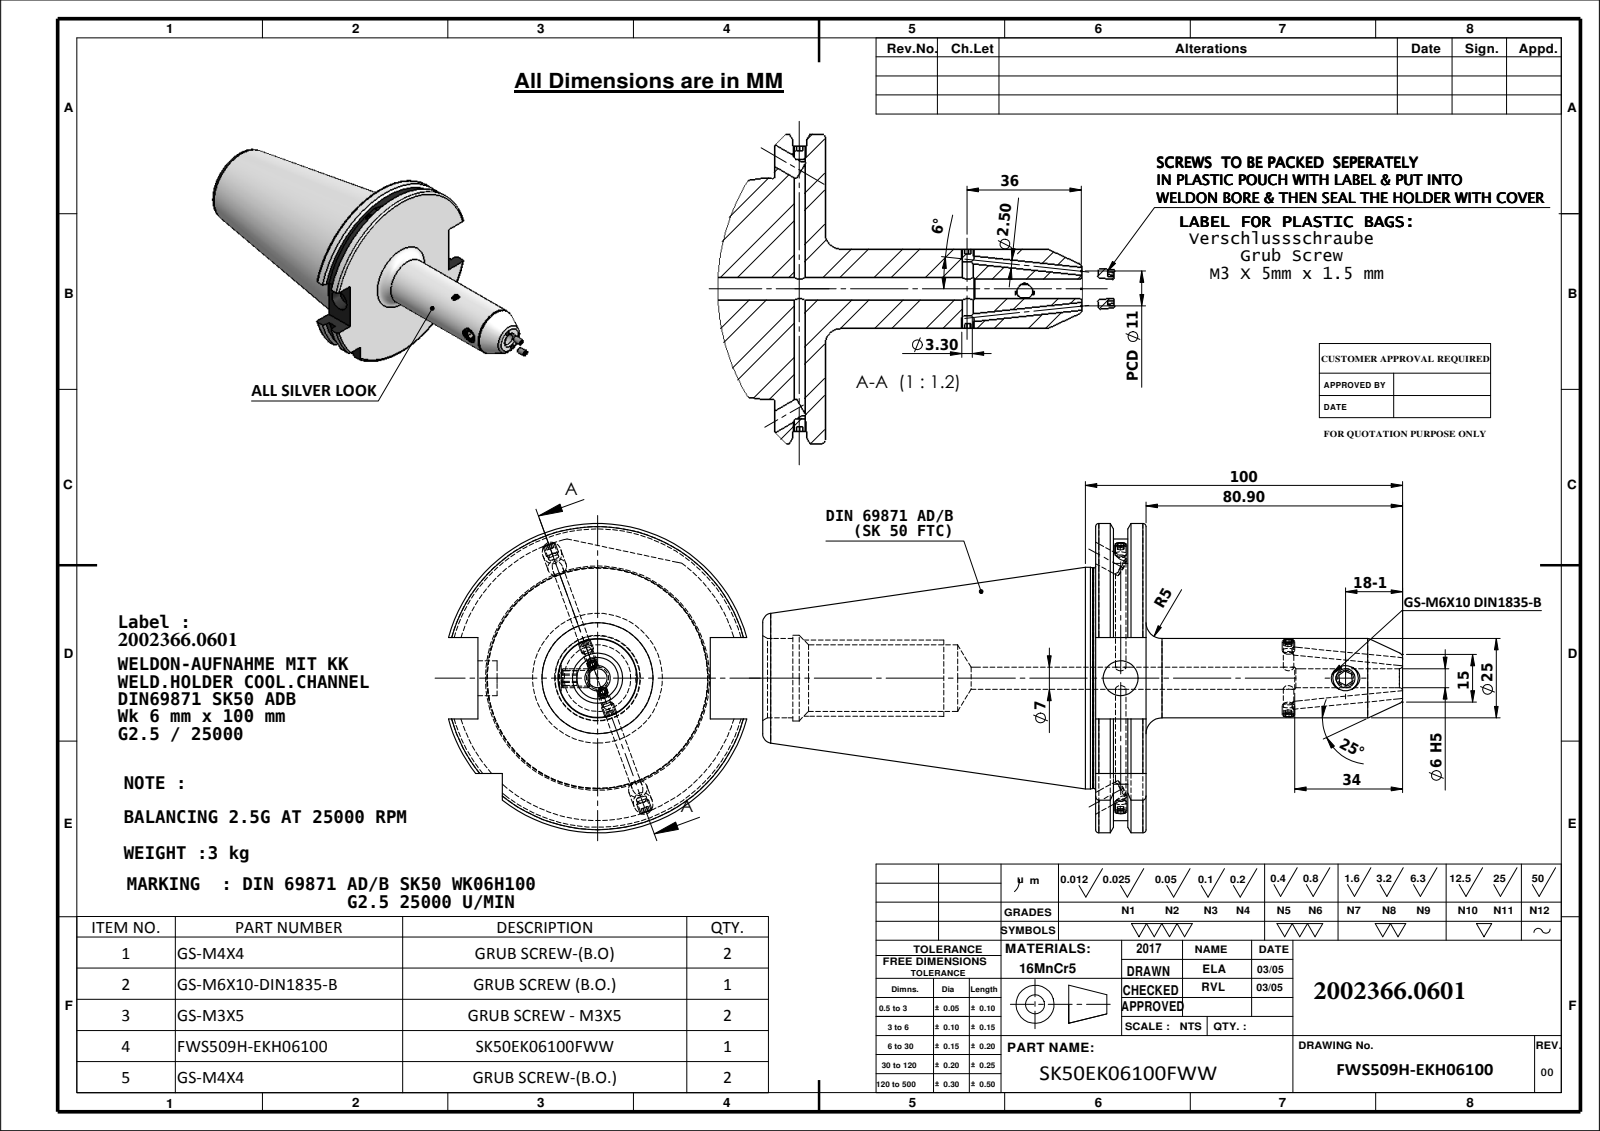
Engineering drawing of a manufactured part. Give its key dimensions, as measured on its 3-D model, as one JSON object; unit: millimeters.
{"part_name": "Copy of M4X4_DIN 913 - M4 x 4-N; M3X5_DIN 913 - M3 x 5-N; 91506-WK206100; SK50EK06100FWW (+2 more)", "step_written_by": "SolidWorks 2009 (CONFIG_CONTROL_DESIGN)", "units": "millimeters", "bodies": {"solids": 8, "faces": 233, "planar": 86, "cylindrical": 69, "other": 78}, "overall_size": [211.99, 97.5, 94.05], "volume_mm3": 370567, "surface_area_mm2": 51905, "round_holes": [[6, 3], [2.5, 2], [3.3, 2], [5, 1], [7, 1], [8, 1], [11, 1], [21, 1], [25, 1], [27, 1]], "round_bosses_or_shafts": [[4, 4], [3, 2], [69.85, 1], [69.45, 1], [6, 1]], "partial_cylinders_radius": [[44.9, 1], [48.75, 1]], "face_to_face_distances": [15.9, 5.66, 10.24, 10.15, 4.49, 5.75, 104.95, 110.61, 115.1, 120.85], "hole_center_spacings": [52.9, 70.9]}
